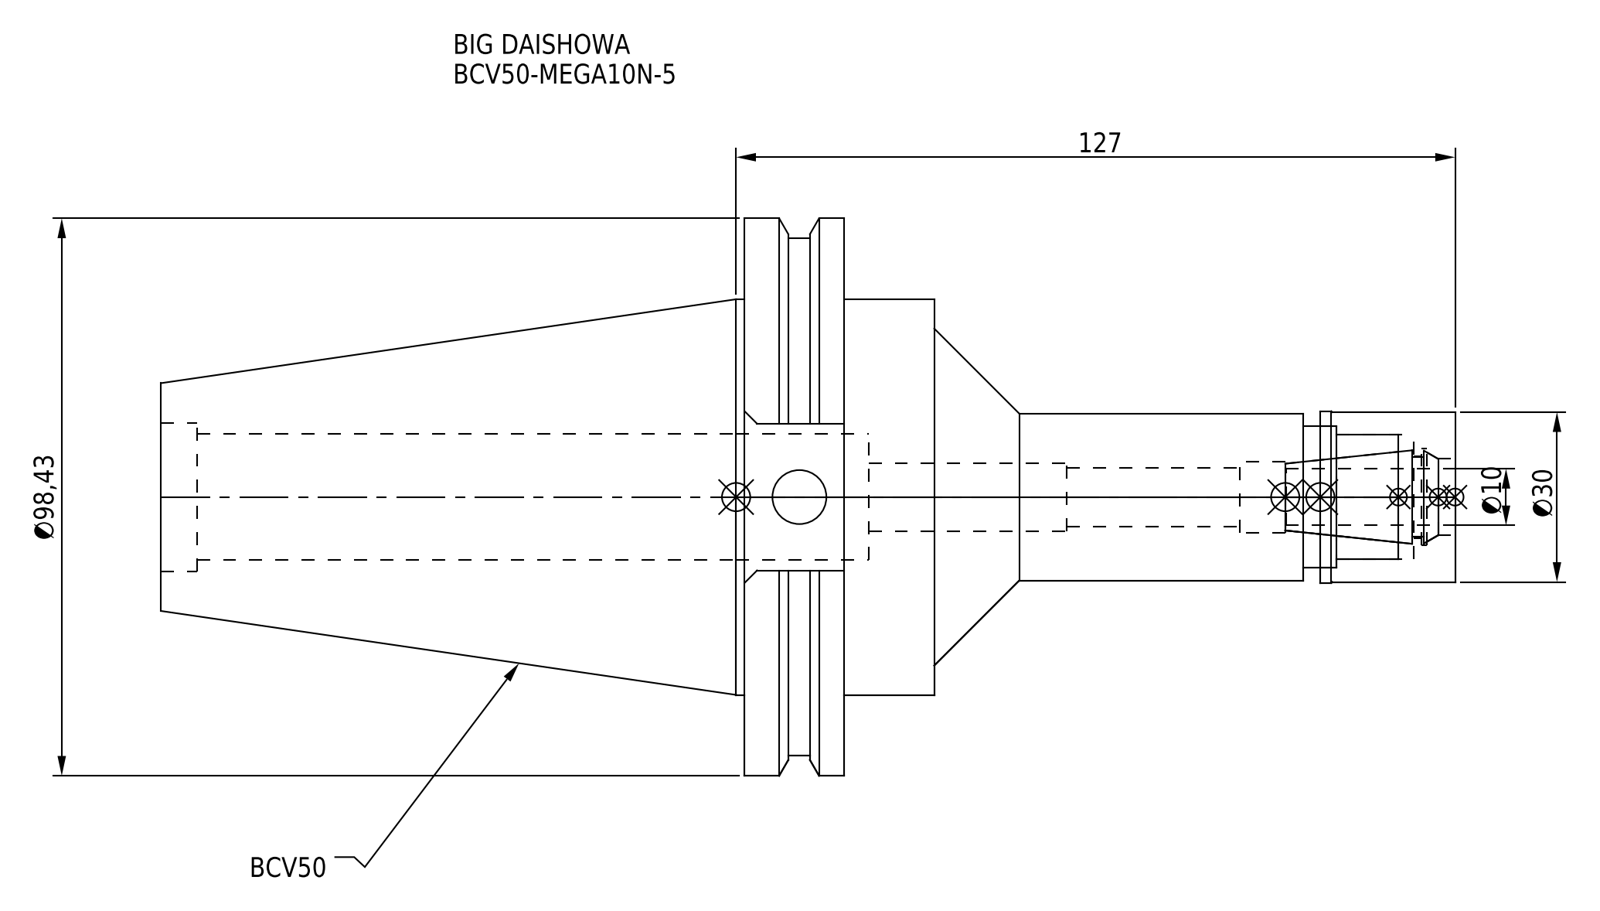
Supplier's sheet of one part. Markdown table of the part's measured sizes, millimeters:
| quantity | value |
| --- | --- |
| part name | BCV50-MEGA10N-5-100.stp; BCV50-MEGA10N-5; DXF_TEMP_ASSY_ASM_4_ASM.stp; BCV50-MEGA10N-5-100-FreeParts (+3 more) |
| STEP written by | SolidWorks 2019 (CONFIG_CONTROL_DESIGN) |
| units | millimeters |
| bodies | 2 solids, 91 faces (33 planar, 44 cylindrical, 14 other) |
| overall size | 228.6 × 98.42 × 94.95 |
| volume | 446 480 mm³ |
| surface area | 63 922 mm² |
| round holes (diameter × count) | 9.53 × 1, 10.4 × 1, 12 × 1, 12.5 × 1, 13.5 × 1, 14.5 × 1, 17 × 1, 22 × 1, 22.3 × 1, 25 × 1, 26.23 × 1 |
| round bosses / shafts (diameter × count) | 98.42 × 1, 91.29 × 1, 69.85 × 1, 30.3 × 1, 30 × 1, 29.5 × 1 |
| main face-to-face distances | 17.55, 15.95, 33.5, 136.6, 120.65, 103.1, 107.95, 92, 125.5, 228.6 |
